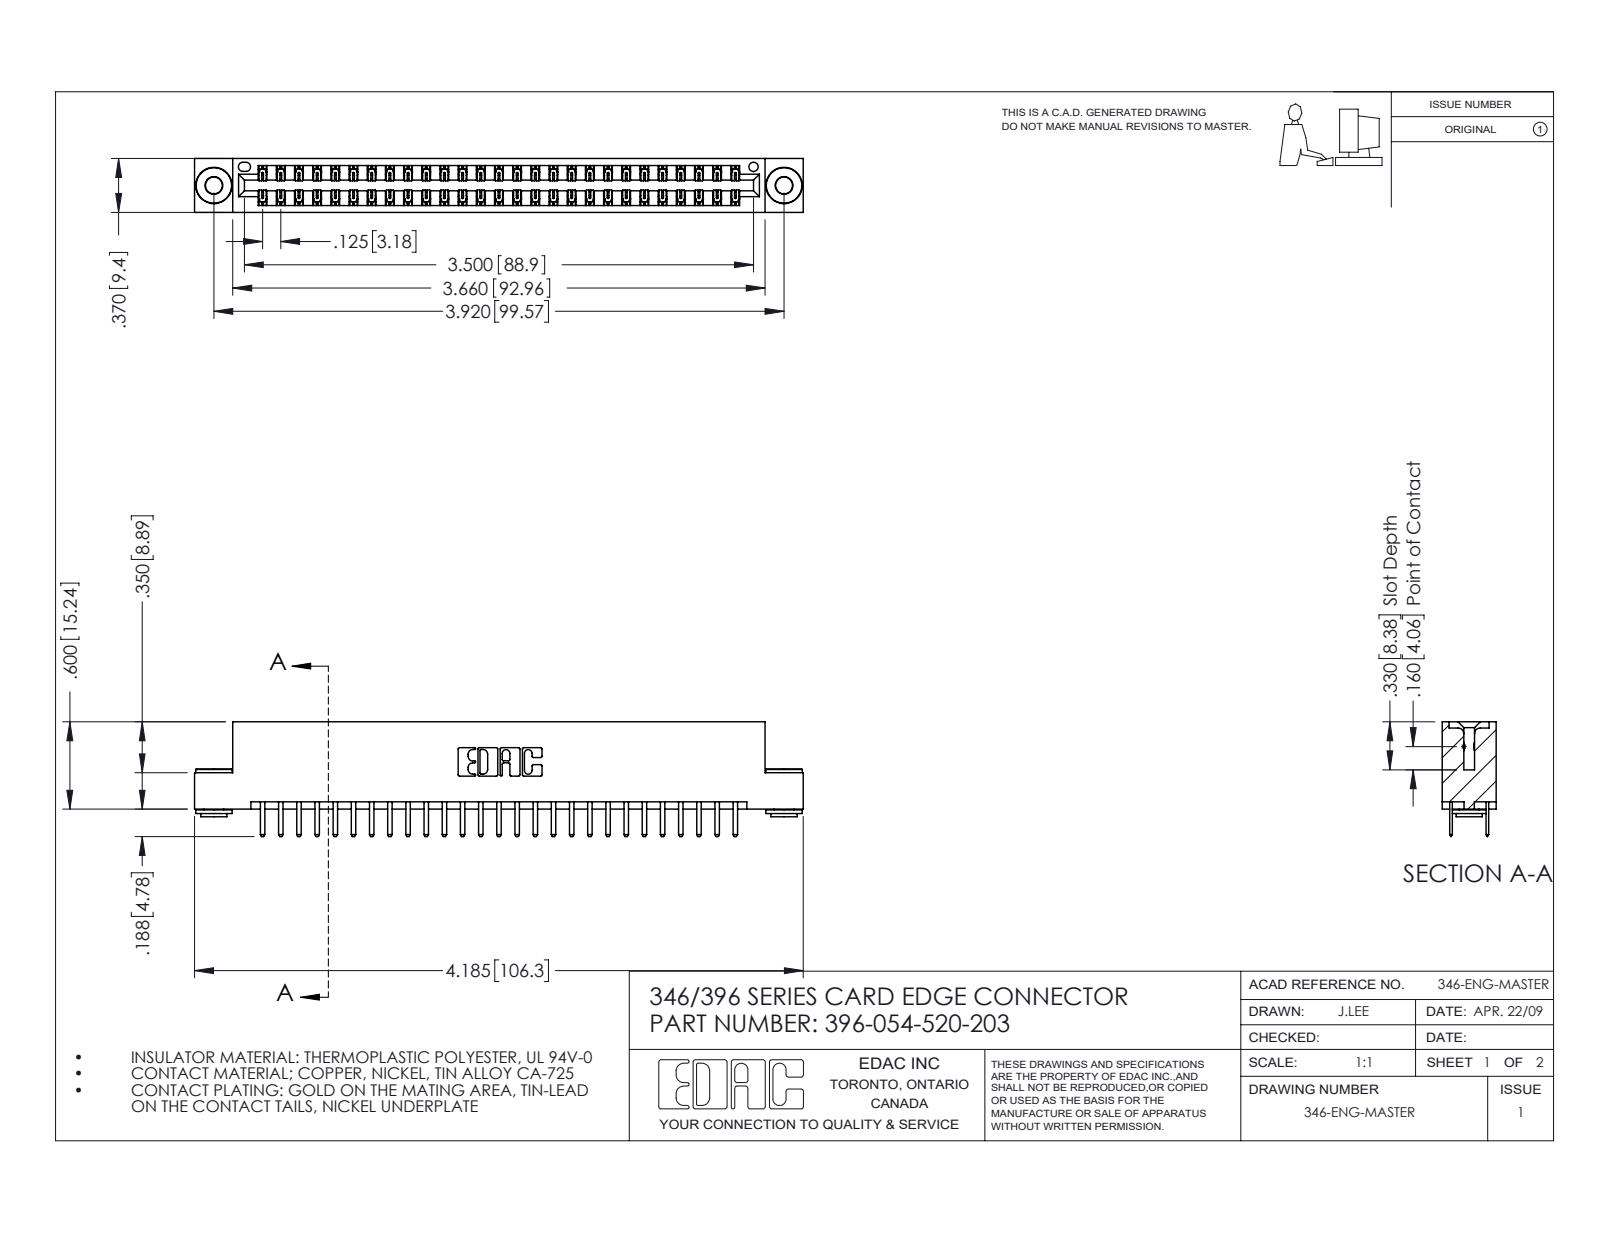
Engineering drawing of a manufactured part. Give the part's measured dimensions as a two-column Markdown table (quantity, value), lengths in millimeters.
| quantity | value |
| --- | --- |
| part name | 345-292-001_345-293-120; 345-250-002_345-250-002-102; 396-054-520-203; 346 Part_Flush Mounting Lugs - 0.156 Dia-TH |
| STEP written by | SolidWorks 2016 (CONFIG_CONTROL_DESIGN) |
| units | millimeters |
| bodies | 57 solids, 3184 faces (2084 planar, 1092 cylindrical, 8 other) |
| overall size | 106.3 × 20 × 9.4 |
| volume | 10 200 mm³ |
| surface area | 14 010 mm² |
| round holes (diameter × count) | 2.9 × 2, 4 × 2, 1.6 × 1 |
| round bosses / shafts (diameter × count) | 6.4 × 2, 4.6 × 2, 3.5 × 2 |
| partial cylindrical surfaces (radius × count) | 0.2 × 81, 0.3 × 58, 0.3 × 22, 0.2 × 6, 0.8 × 6, 0.7 × 3, 0.4 × 2, 0.6 × 2 |
| main face-to-face distances | 1.2, 8.2, 6.4, 9.4, 0.6, 7, 1.8, 7.6, 3.8, 5.6 |
| hole center spacings | 6.2, 94.3, 99.6 |
